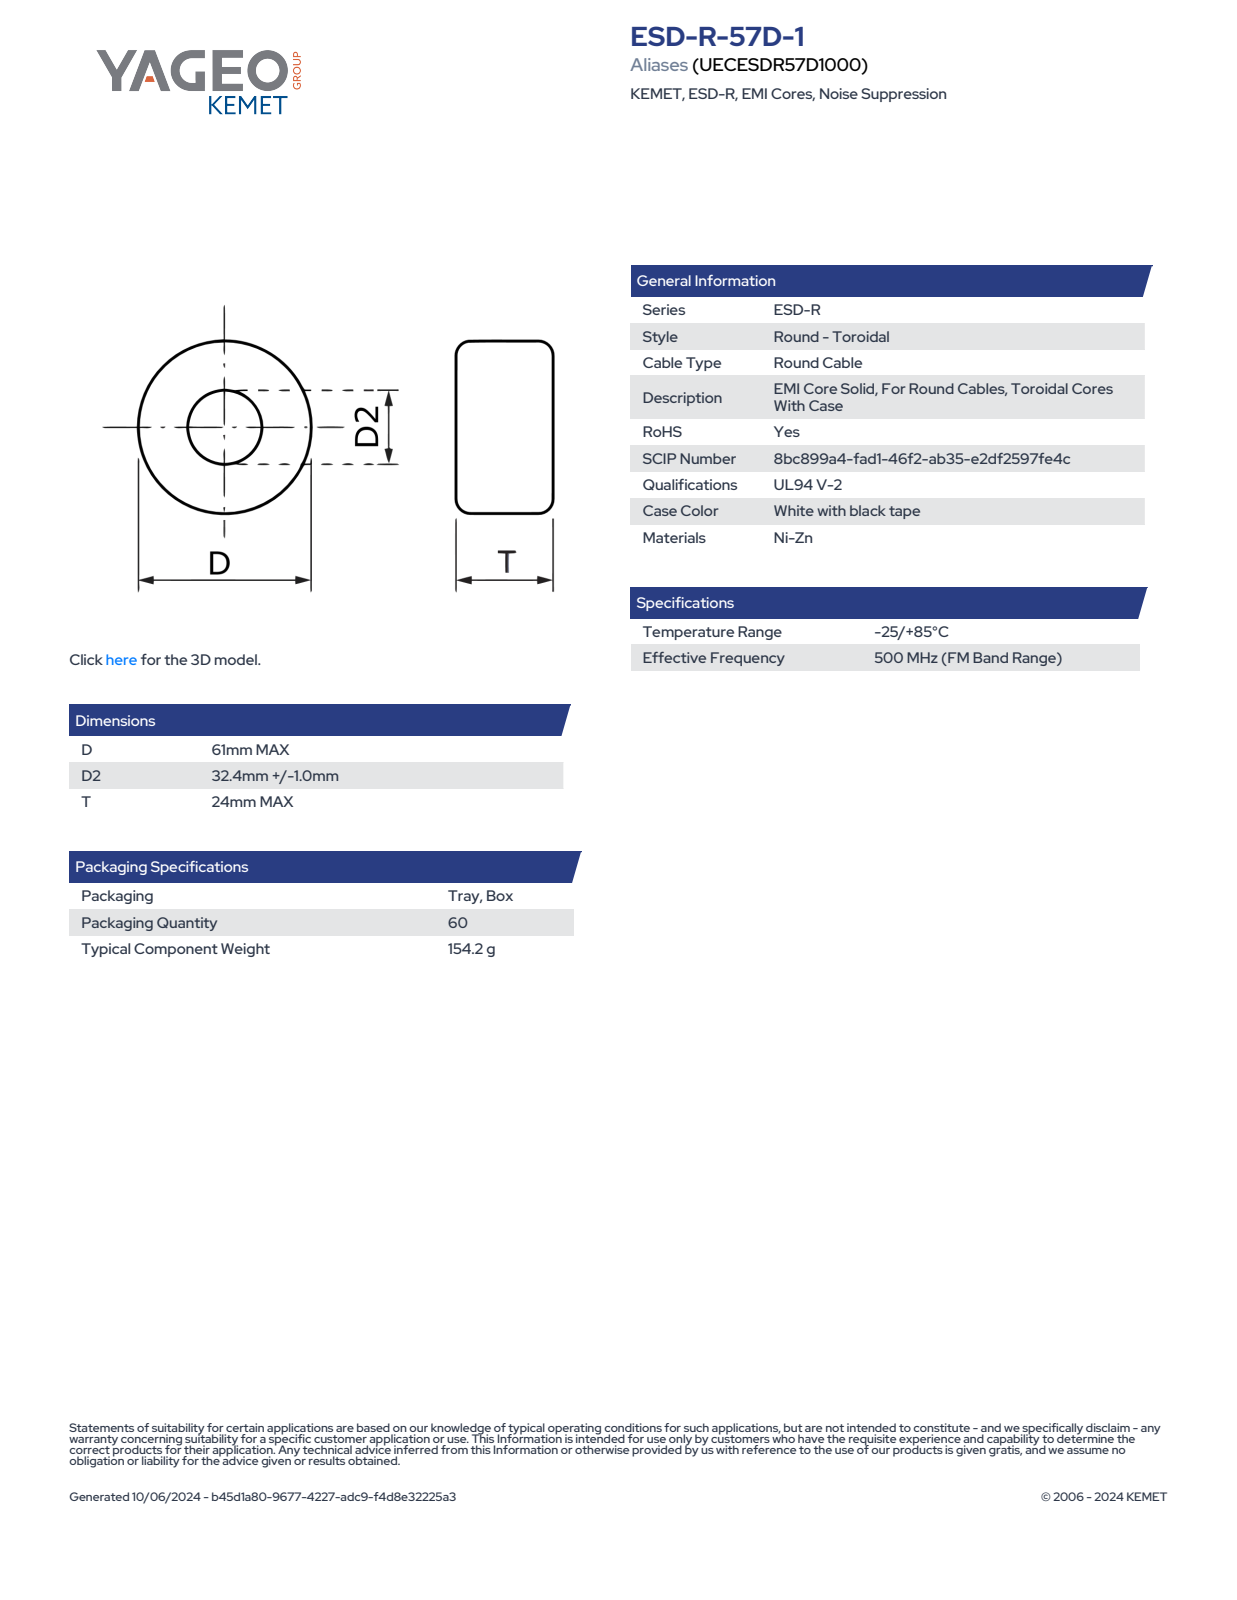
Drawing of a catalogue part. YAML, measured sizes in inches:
part_name: "EC_KBC_D61D232.4T24"
step_written_by: "SolidWorks 2021 (AUTOMOTIVE_DESIGN)"
units: inches
bodies: {solids: 1, faces: 66, planar: 24, cylindrical: 7, other: 35}
overall_size: [2.402, 2.402, 0.945]
volume: 3.054
surface_area: 16.98
round_holes:
  - {diameter: 1.276, count: 1}
round_bosses_or_shafts:
  - {diameter: 2.402, count: 1}
partial_cylinders:
  - {radius: 1.201, count: 1}
face_to_face_distances: [0.945, 0.439, 0.506, 0.067, 0.013, 0.452, 0.493, 0.054, 0.042, 0.481]
